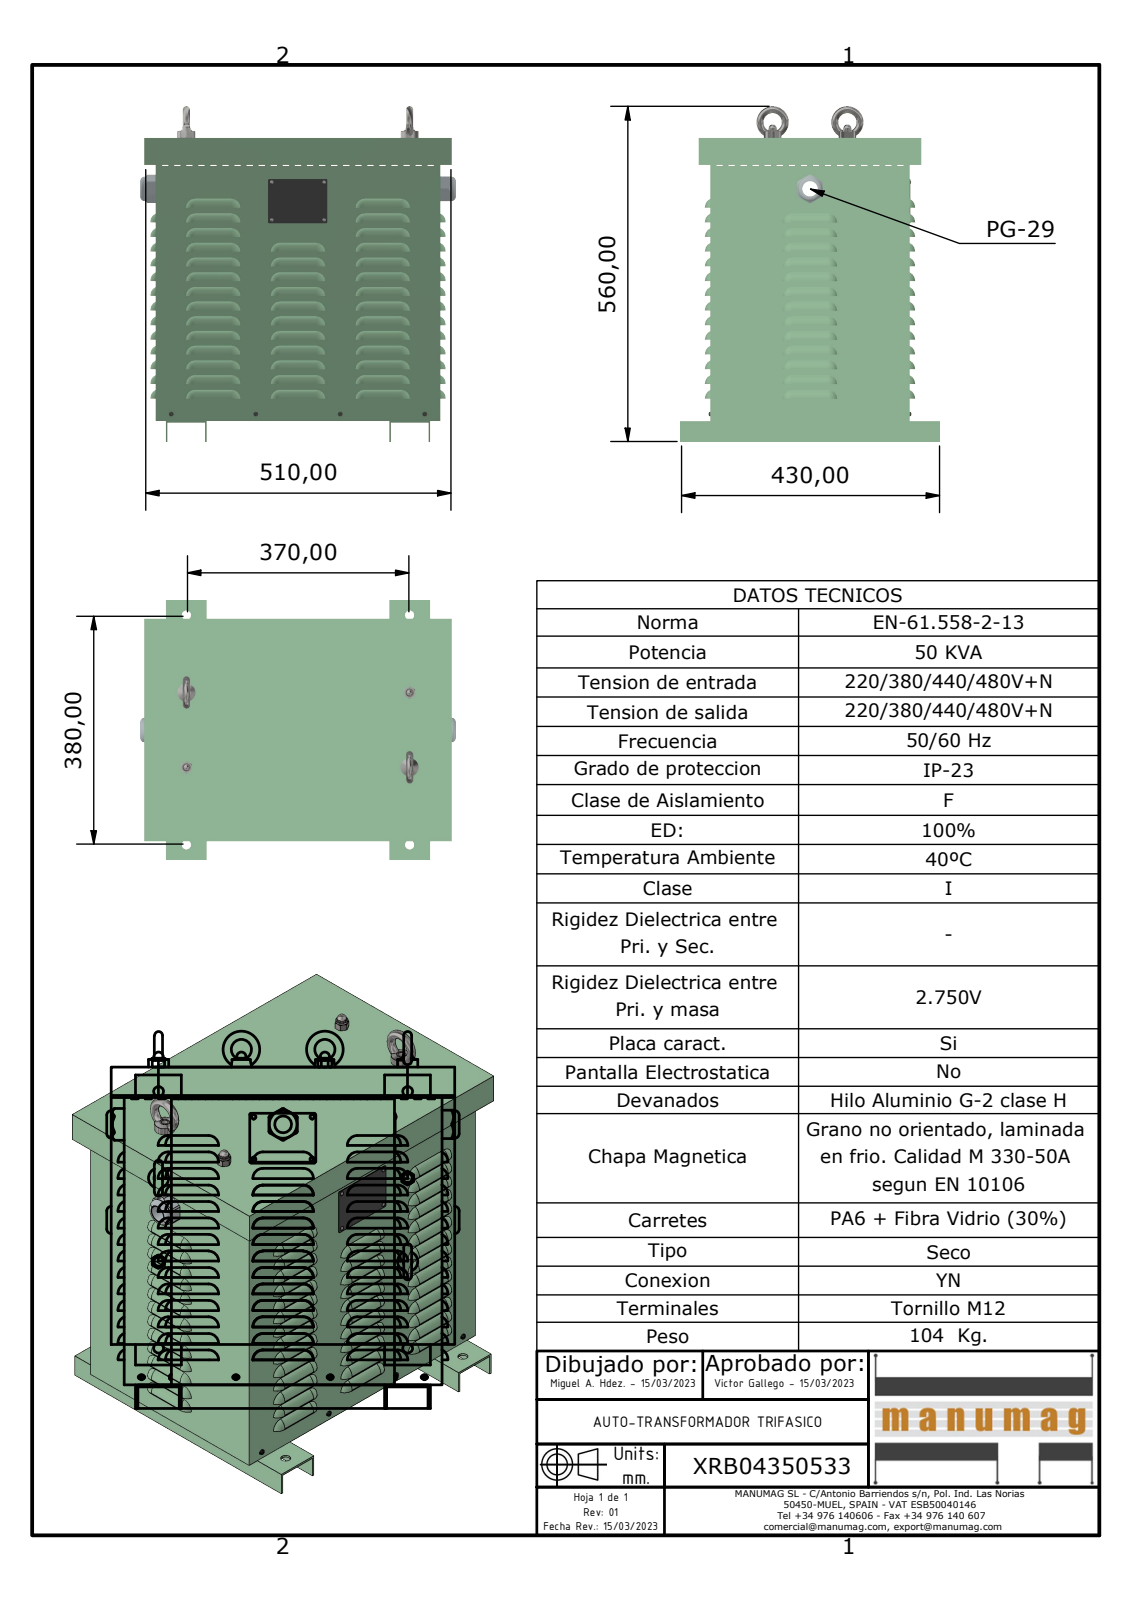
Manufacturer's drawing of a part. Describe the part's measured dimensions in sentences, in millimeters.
The part is named "XRB04350533; JE040 - JE050 CUERPO; JE040 - JE050 BASE; JE040 - JE050 PATAS (+7 more)". Its 3-D file was written by "Autodesk Inventor 2023 (AUTOMOTIVE_DESIGN)". It is 24 solids with 2403 faces: 969 planar, 808 cylindrical and 626 other. Overall it measures 560 by 523.4 by 431 millimeters. Its volume is 3 115 000 cubic millimeters and its surface area 2 768 000 square millimeters. Round holes: 260 of diameter 11, 4 of diameter 4, 4 of diameter 5, 4 of diameter 10.11, 4 of diameter 14, 4 of diameter 15, 1 of diameter 25, 1 of diameter 38. Round bosses or shafts: 4 of diameter 4, 4 of diameter 3.62, 4 of diameter 3.2, 2 of diameter 30, 2 of diameter 18, 2 of diameter 13.6, 1 of diameter 40.8, 1 of diameter 37.3. Partial cylindrical surfaces (rounded edges, fillets, slot ends): 104 of radius 14, 54 of radius 7, 54 of radius 15, 12 of radius 3.22, 8 of radius 2.5, 8 of radius 7.5, 4 of radius 2, 1 of radius 23.85. The main face-to-face distances are 2, 470, 472, 329, 468, 327, 331, 3, 19.5, 348.5. The hole center spacings are 31.76, 71.59, 15, 28, 70, 44.6, 99.14, 140.8.
